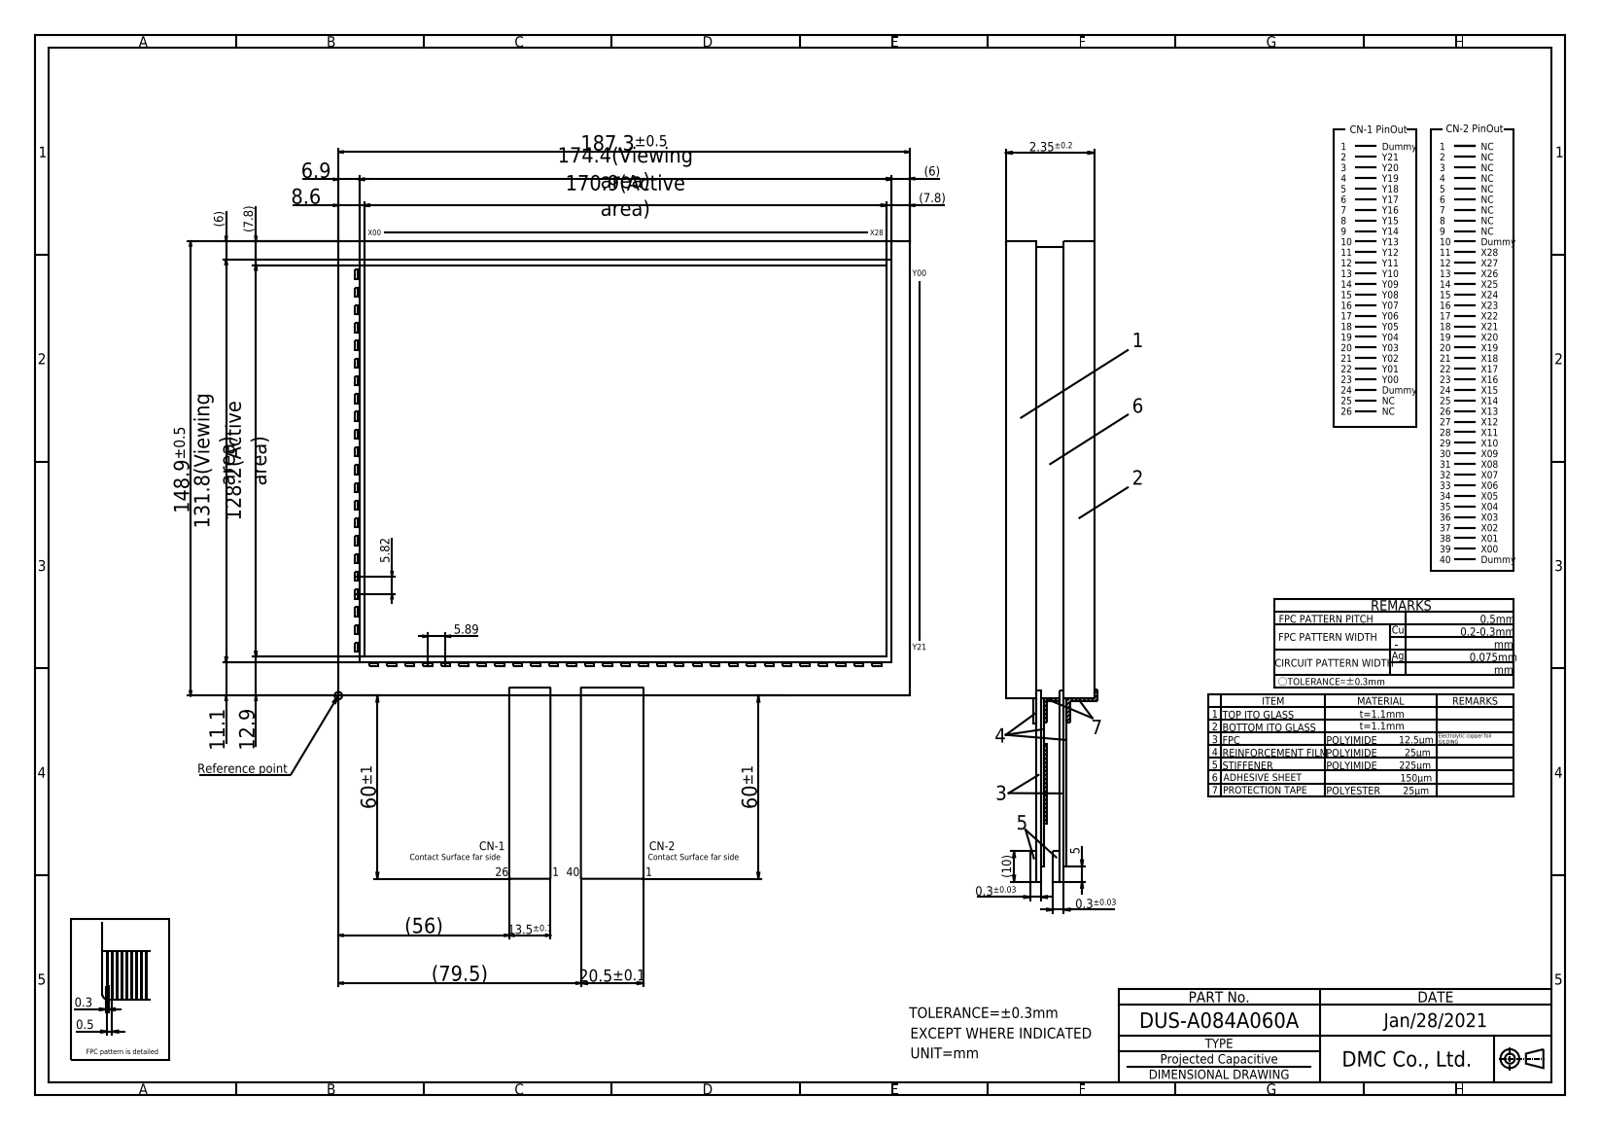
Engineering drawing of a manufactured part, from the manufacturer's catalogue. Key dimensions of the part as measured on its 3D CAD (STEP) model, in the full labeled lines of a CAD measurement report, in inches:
Part name (STEP PRODUCT): DUS-A084A060A
STEP written by: Autodesk Inventor 2020 (CONFIG_CONTROL_DESIGN)
Units: inches
Bodies: 1 solid, 302 faces (298 planar, 4 cylindrical, 0 other)
Overall size (bounding box): 10.324 × 9.397 × 0.093
Volume: 4.01 in³ · Surface area: 95.51 in²
Partial cylindrical surfaces — rounded edges, fillets, slot ends (radius × count): R0.008 ×4
Main face-to-face distances: 0.093, 0.043, 0.047, 0.045, 0.049, 0.039, 0.089, 5.862, 7.374, 0.031
